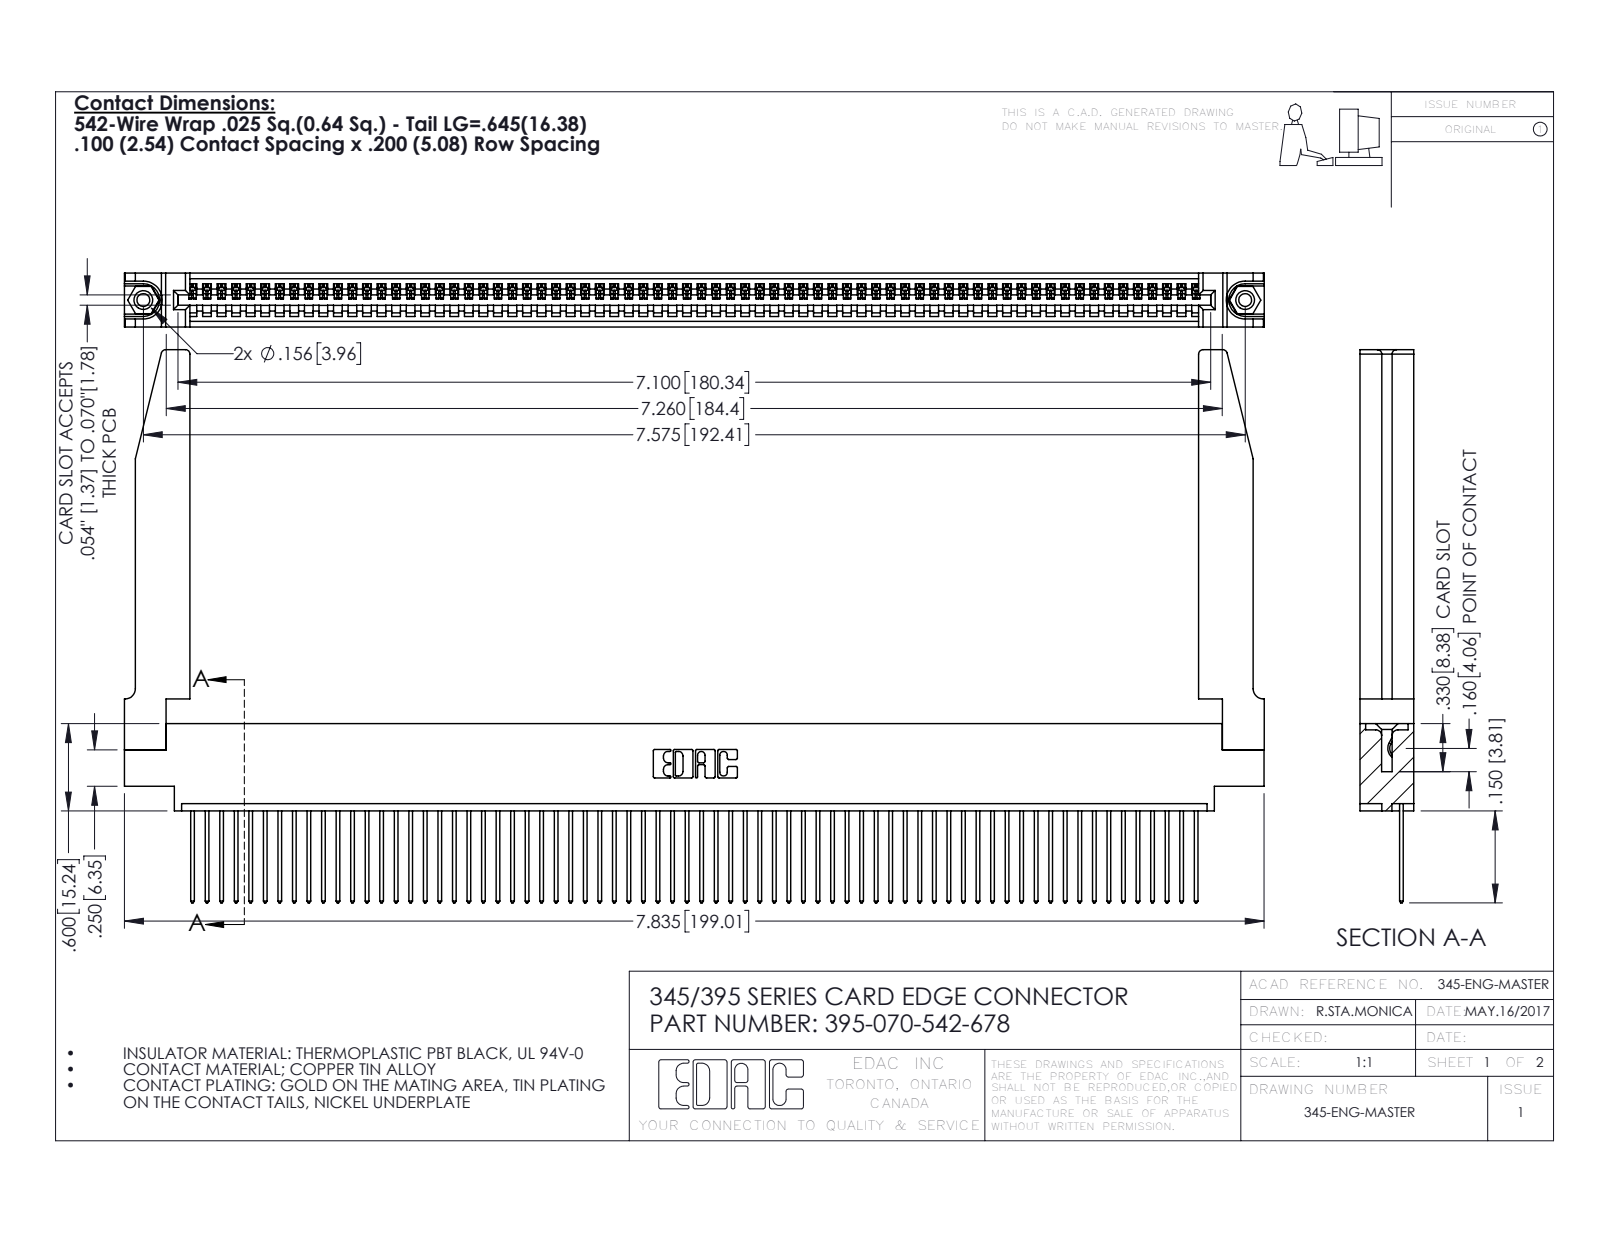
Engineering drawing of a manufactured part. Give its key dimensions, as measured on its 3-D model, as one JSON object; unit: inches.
{"part_name": "345-250-001_345-250-001-102; 345-220-078_345-220-078; 395-070-542-678; 345-292-001_345-293-142 (+1 more)", "step_written_by": "SolidWorks 2016 (CONFIG_CONTROL_DESIGN)", "units": "inches", "bodies": {"solids": 75, "faces": 4424, "planar": 3026, "cylindrical": 1346, "other": 52}, "overall_size": [7.836, 3.802, 0.37], "volume_in3": 1.644, "surface_area_in2": 52.42, "round_holes": [[0.089, 2], [0.125, 2], [0.156, 2], [0.064, 1]], "round_bosses_or_shafts": [[0.155, 2]], "partial_cylinders_radius": [[0.006, 140], [0.01, 140], [0.01, 22], [0.03, 8], [0.007, 6], [0.031, 6], [0.026, 3], [0.031, 2]], "face_to_face_distances": [0.072, 0.298, 0.37, 0.098, 0.272, 0.025, 0.2, 0.225, 0.175, 0.149], "hole_center_spacings": [0.27, 7.339, 7.575]}
